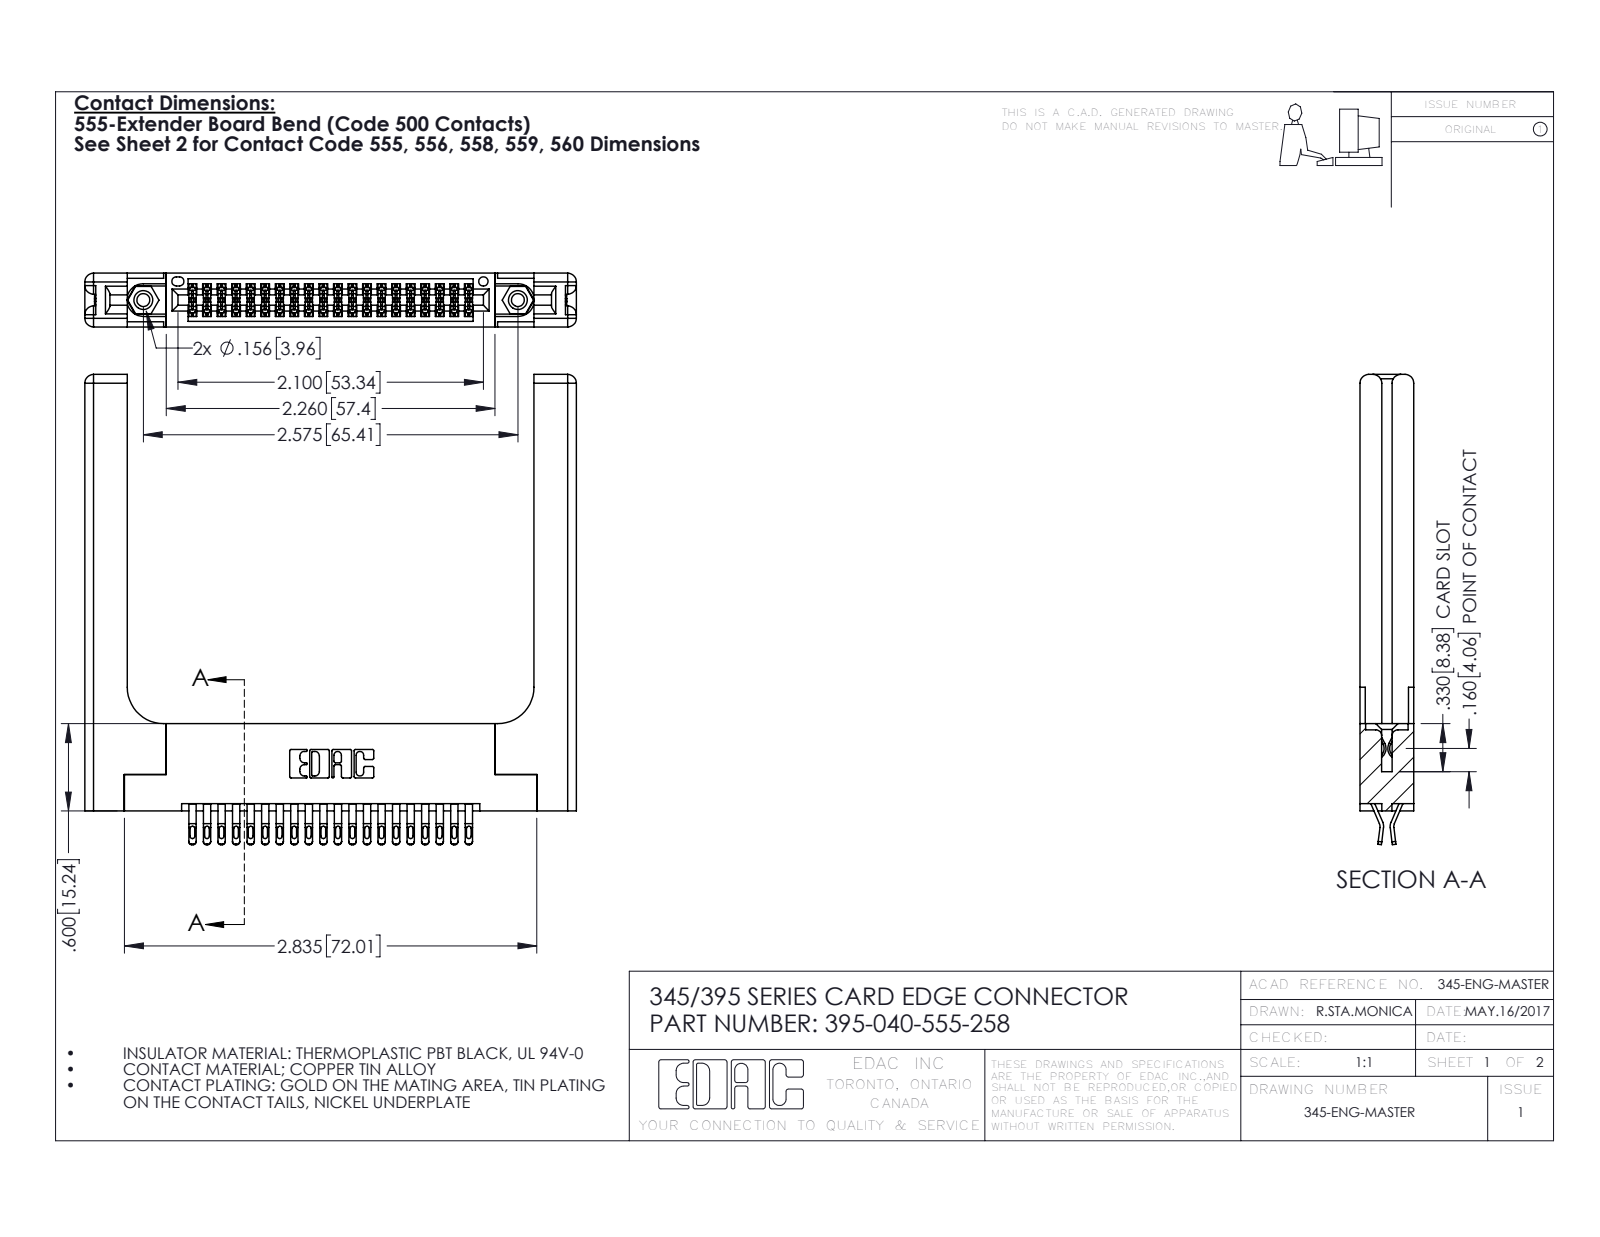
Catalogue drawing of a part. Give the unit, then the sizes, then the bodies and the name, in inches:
Units: inches
Overall size (bounding box): 3.379 × 3.232 × 0.37
Round holes (diameter × count): ⌀0.089 ×2, ⌀0.125 ×2, ⌀0.156 ×2, ⌀0.064 ×1
Round bosses / shafts (diameter × count): ⌀0.155 ×2
Partial cylindrical surfaces — rounded edges, fillets, slot ends (radius × count): R0.016 ×100, R0.02 ×80, R0.006 ×60, R0.01 ×22, R0.06 ×16, R0.007 ×6, R0.031 ×6, R0.026 ×3
Main face-to-face distances: 0.37, 0.072, 0.298, 0.2, 0.148, 0.15, 0.077, 0.025, 0.22, 0.225
Hole centre spacings: 0.27, 2.341, 2.575
Volume: 1.021 in³ · Surface area: 26.71 in²
Bodies: 45 solids, 2622 faces (1468 planar, 1094 cylindrical, 60 other)
Part name (STEP PRODUCT): 345-292-001_555 Tail; 395-040-555-258; 345-250-001_345-250-001-102; 345-220-058_345-220-058 (+1 more)
STEP written by: SolidWorks 2016 (CONFIG_CONTROL_DESIGN)
